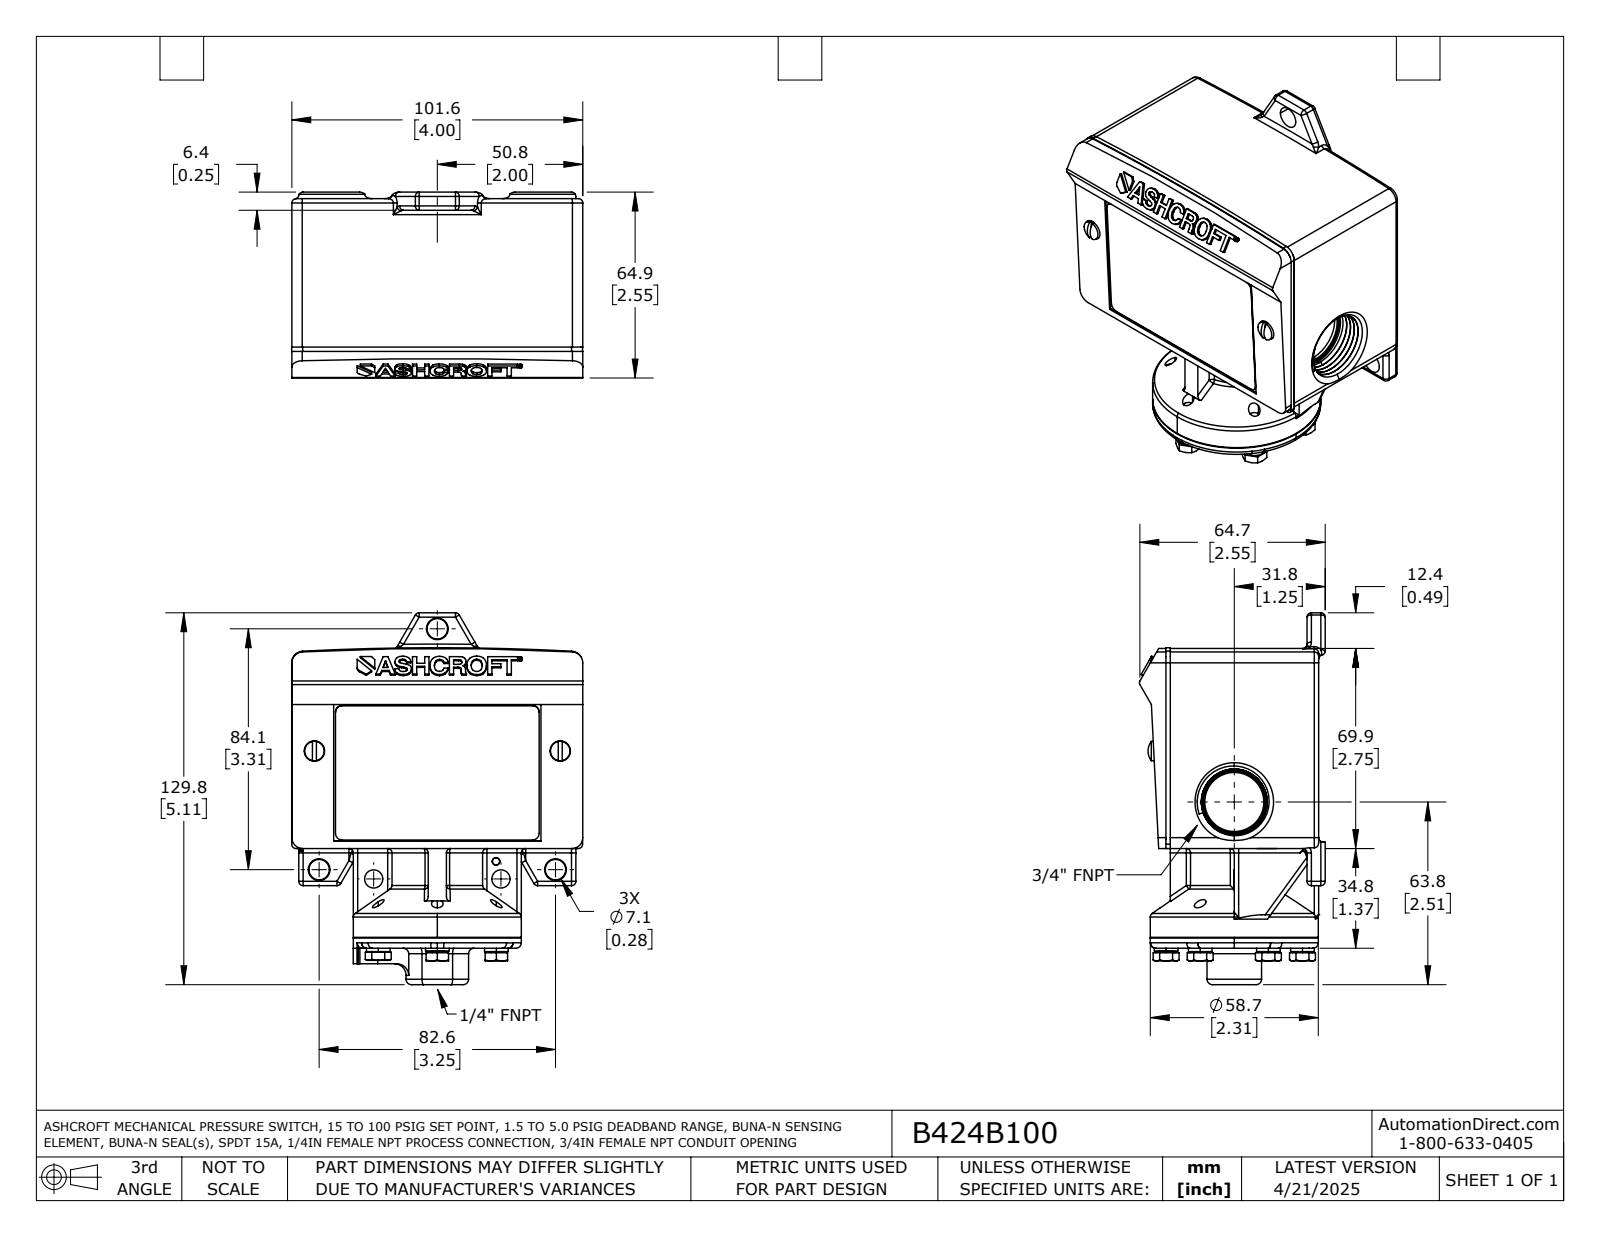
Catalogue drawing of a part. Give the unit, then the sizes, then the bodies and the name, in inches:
Units: inches
Overall size (bounding box): 5.111 × 4.003 × 2.555
Round holes (diameter × count): ⌀0.161 ×6, ⌀0.192 ×5, ⌀0.209 ×5, ⌀0.187 ×4, ⌀0.28 ×2, ⌀0.455 ×1, ⌀0.812 ×1
Round bosses / shafts (diameter × count): ⌀0.325 ×6, ⌀0.278 ×6, ⌀0.19 ×5, ⌀0.27 ×2, ⌀0.25 ×2, ⌀2.31 ×1
Partial cylindrical surfaces — rounded edges, fillets, slot ends (radius × count): R0.06 ×92, R0.03 ×5, R0.075 ×4, R0.09 ×4, R0.15 ×4, R0.01 ×2, R0.094 ×2, R0.16 ×2
Main face-to-face distances: 4, 0.015, 1.37, 0.09, 3.91, 0.44, 3.56, 3.47, 0.35, 0.845
Hole centre spacings: 0.937, 1.624, 1.875, 0.938, 3.38
Volume: 28.57 in³ · Surface area: 84.51 in²
Bodies: 2 solids, 1259 faces (345 planar, 472 cylindrical, 442 other)
Part name (STEP PRODUCT): B424B100
STEP written by: SolidWorks 2021 (AUTOMOTIVE_DESIGN)
